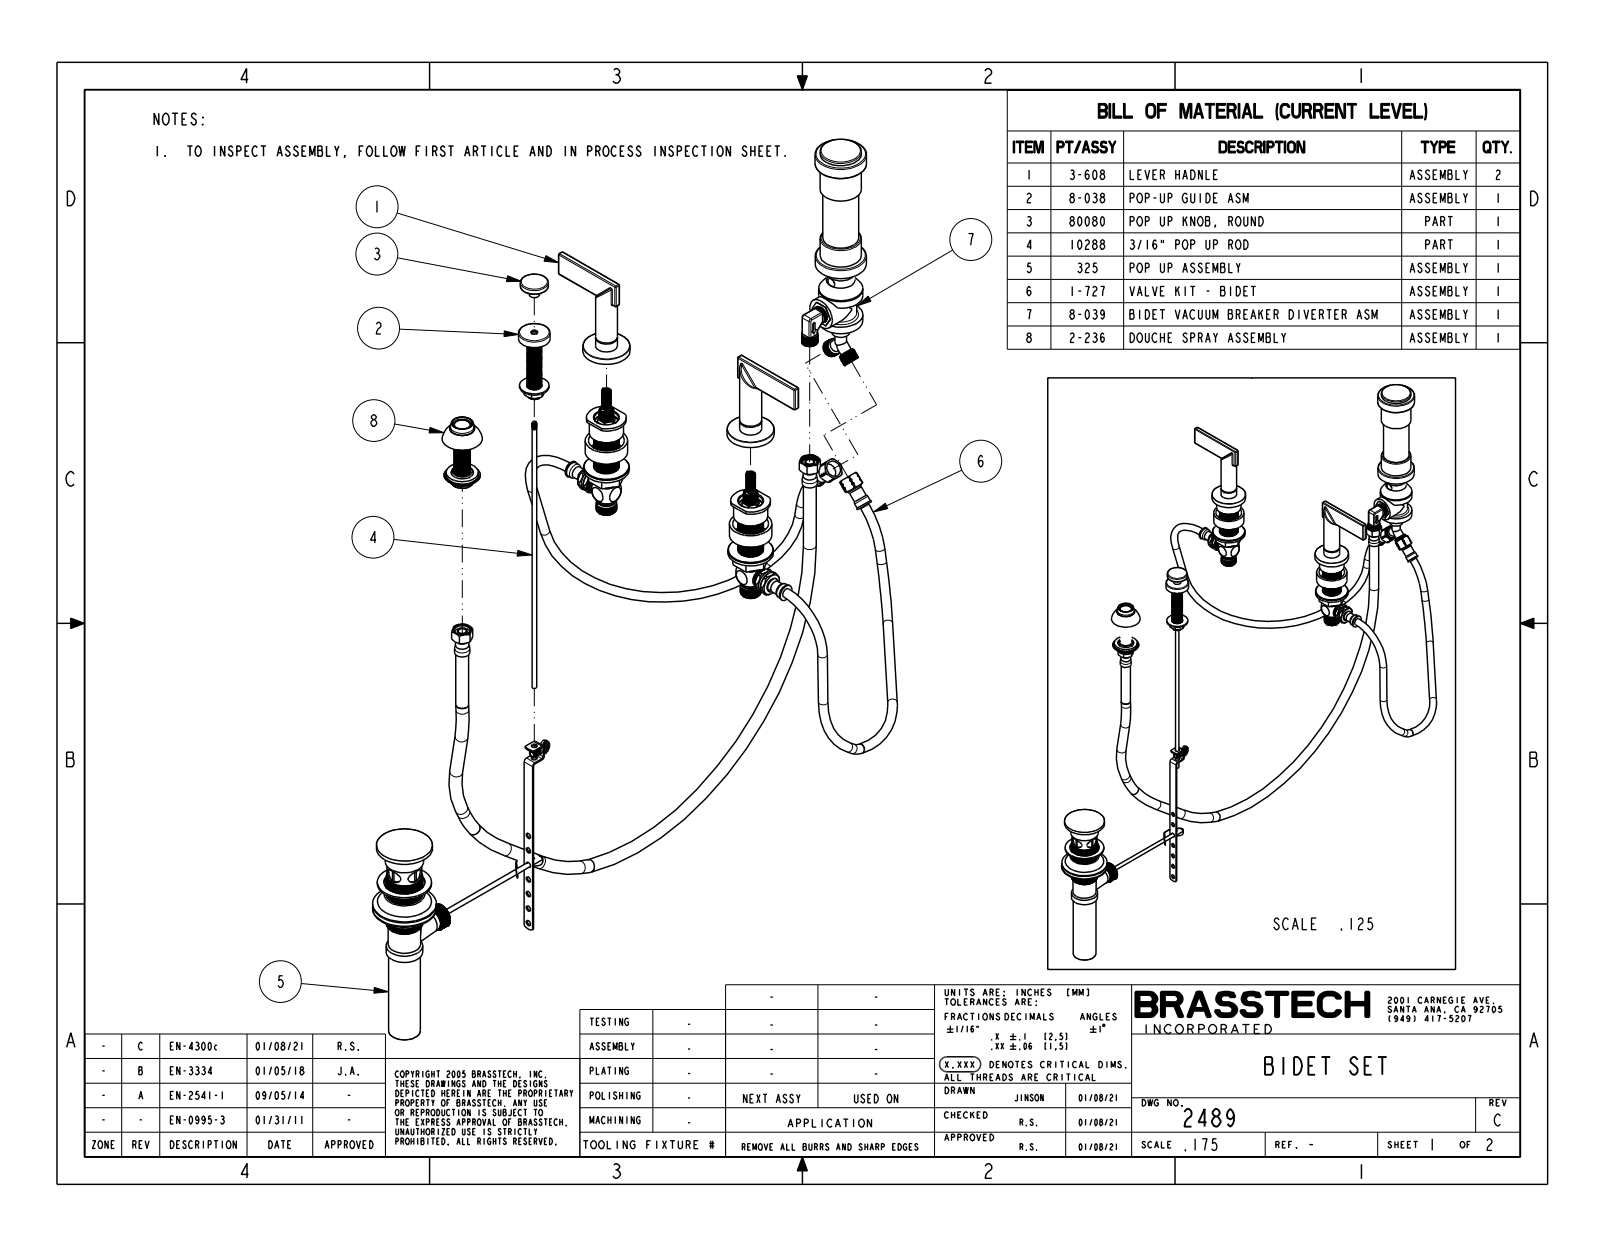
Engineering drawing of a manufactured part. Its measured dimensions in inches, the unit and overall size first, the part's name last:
Units: inches
Overall size (bounding box): 22.8 × 13.12 × 5.445
Round holes (diameter × count): ⌀0.625 ×1, ⌀0.792 ×1, ⌀0.94 ×1
Round bosses / shafts (diameter × count): ⌀1.85 ×2, ⌀0.86 ×2, ⌀0.68 ×2, ⌀2.02 ×1, ⌀2 ×1, ⌀1.62 ×1, ⌀1.4 ×1, ⌀1.24 ×1
Partial cylindrical surfaces — rounded edges, fillets, slot ends (radius × count): R0.04 ×28, R0.357 ×1
Main face-to-face distances: 0.236, 0.25, 5.445, 5.195, 0.31, 0.94, 0.5, 3.2, 3.45, 1.995
Volume: 18.19 in³ · Surface area: 93.2 in²
Bodies: 5 solids, 238 faces (68 planar, 88 cylindrical, 82 other)
Part name (STEP PRODUCT): 2489
STEP written by: CREO PARAMETRIC BY PTC INC, 2018400 (CONFIG_CONTROL_DESIGN)
